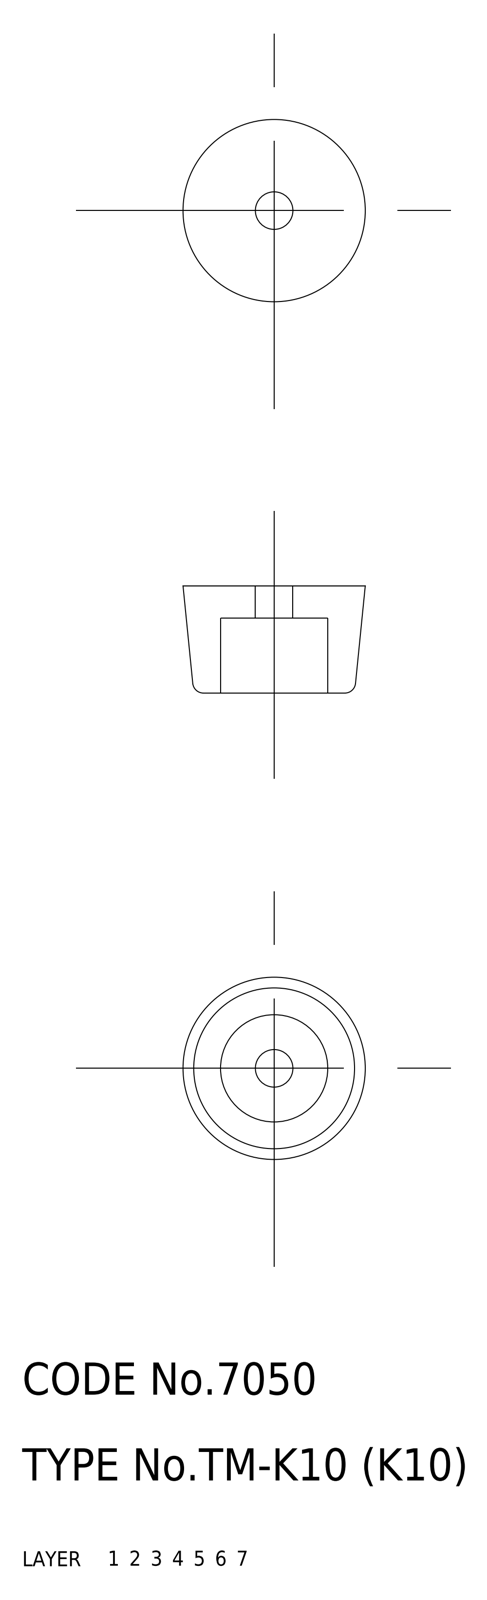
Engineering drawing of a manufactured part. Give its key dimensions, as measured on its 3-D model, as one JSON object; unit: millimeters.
{"part_name": "rubber foot", "step_written_by": "CADfix (AUTOMOTIVE_DESIGN)", "units": "millimeters", "bodies": {"solids": 1, "faces": 11, "planar": 0, "cylindrical": 0, "other": 11}, "overall_size": [17, 17, 10], "volume_mm3": 1431, "surface_area_mm2": 1127}
